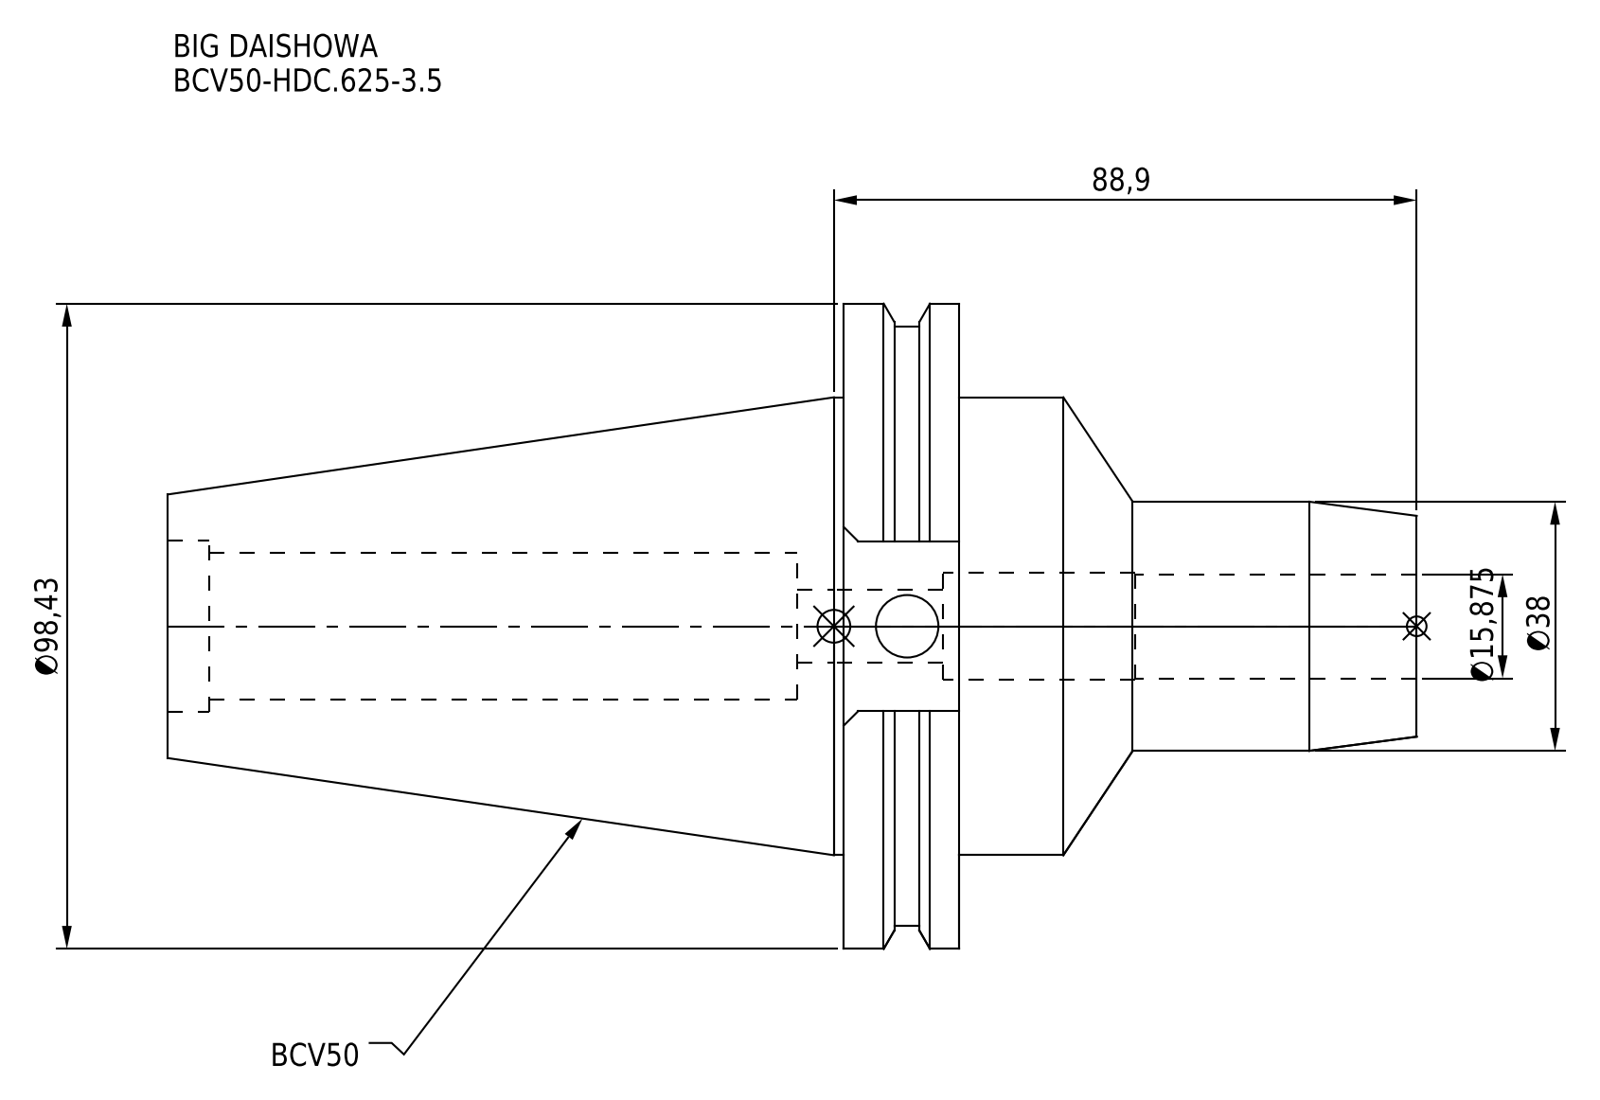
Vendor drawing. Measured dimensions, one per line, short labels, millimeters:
name: BCV50-HDC_625-3_5
written by: CREO PARAMETRIC BY PTC INC, 2016380 (AUTOMOTIVE_DESIGN)
unit: mm
bodies: 1 solid, 59 faces (23 planar, 26 cylindrical, 10 other)
size: 190.5 × 98.42 × 94.95
volume: 448 971 mm³; area: 56 530 mm²
holes: 1× ⌀9.53, 1× ⌀11, 1× ⌀15.88, 1× ⌀16.4, 1× ⌀22.3, 1× ⌀26.23
bosses: 1× ⌀98.42, 1× ⌀91.29, 1× ⌀69.85, 1× ⌀38
face distances: 17.55, 120.65, 103.1, 69.85, 87.4, 190.5, 72.95, 25.92, 94.5, 24.65
